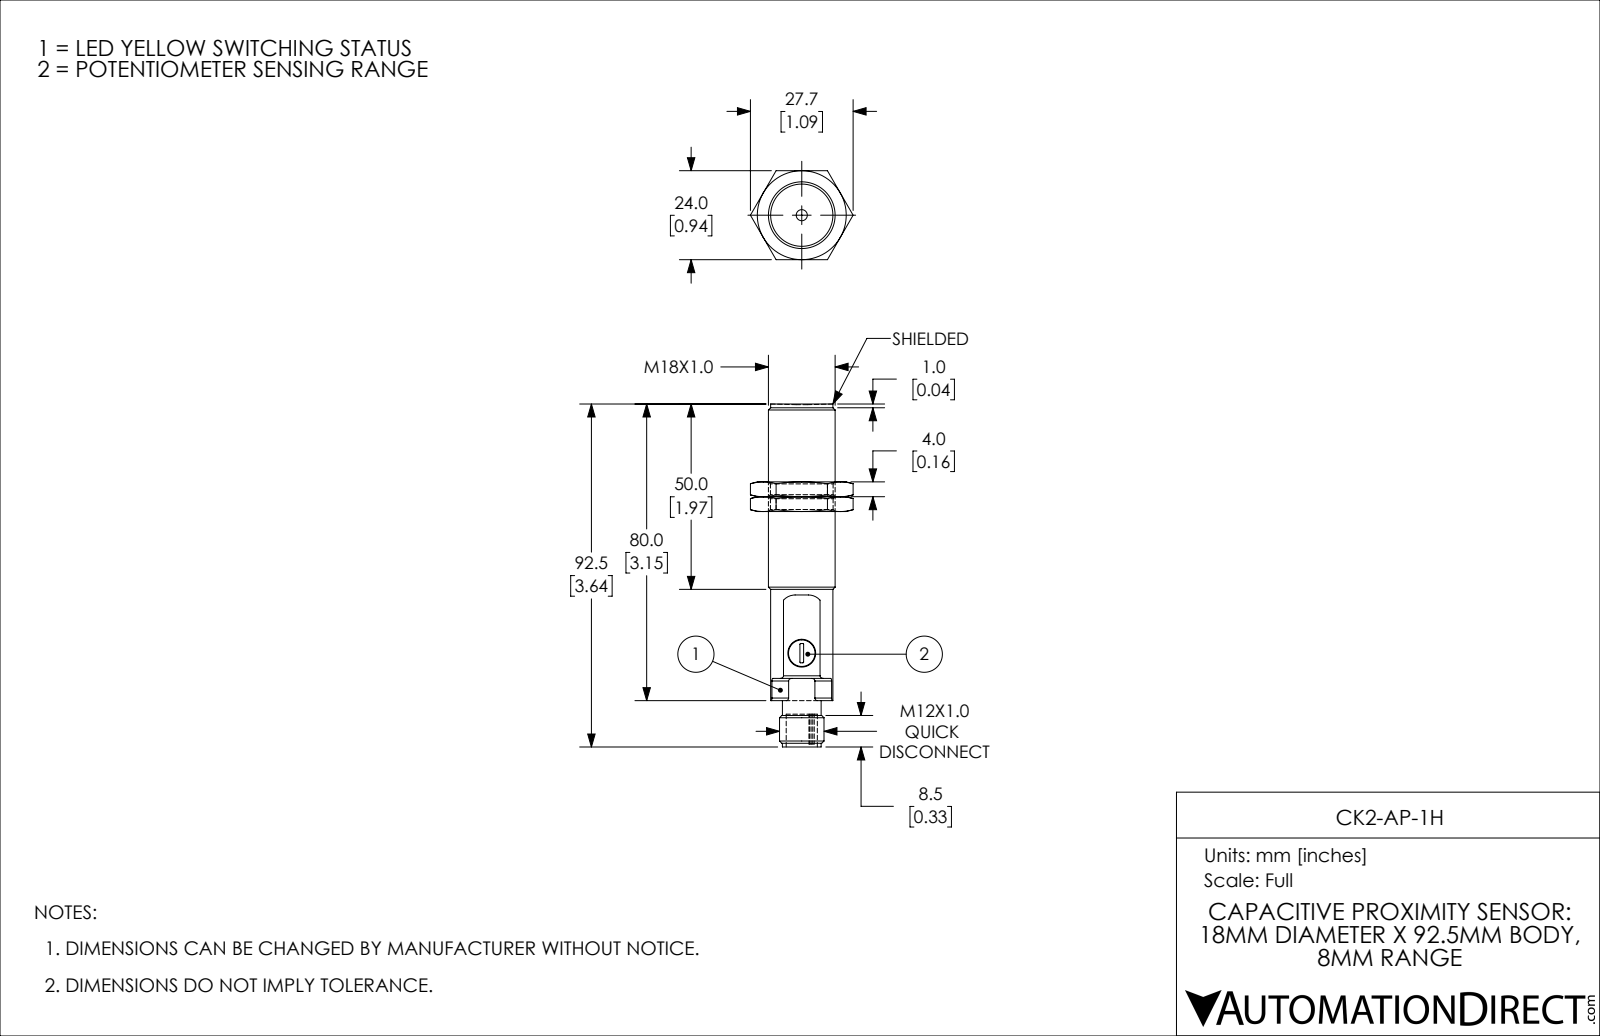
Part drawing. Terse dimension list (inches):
name: CK2-AP-1H_0kb
written by: SolidWorks 2018 (AUTOMOTIVE_DESIGN)
unit: in
bodies: 3 solids, 92 faces (35 planar, 22 cylindrical, 35 other)
size: 3.642 × 1.091 × 0.945
volume: 1.319 in³; area: 11.83 in²
holes: 1× ⌀0.331, 1× ⌀0.666
bosses: 1× ⌀0.709, 1× ⌀0.661, 1× ⌀0.472, 1× ⌀0.411, 1× ⌀0.295
rounds: 4× R0.008, 3× R0.028, 2× R0.165, 1× R0.024
face distances: 0.157, 0.945, 0.315, 0.205, 0.74, 2.165, 2.323, 2.008, 0.144, 2.152
hole spacings: 0.057
